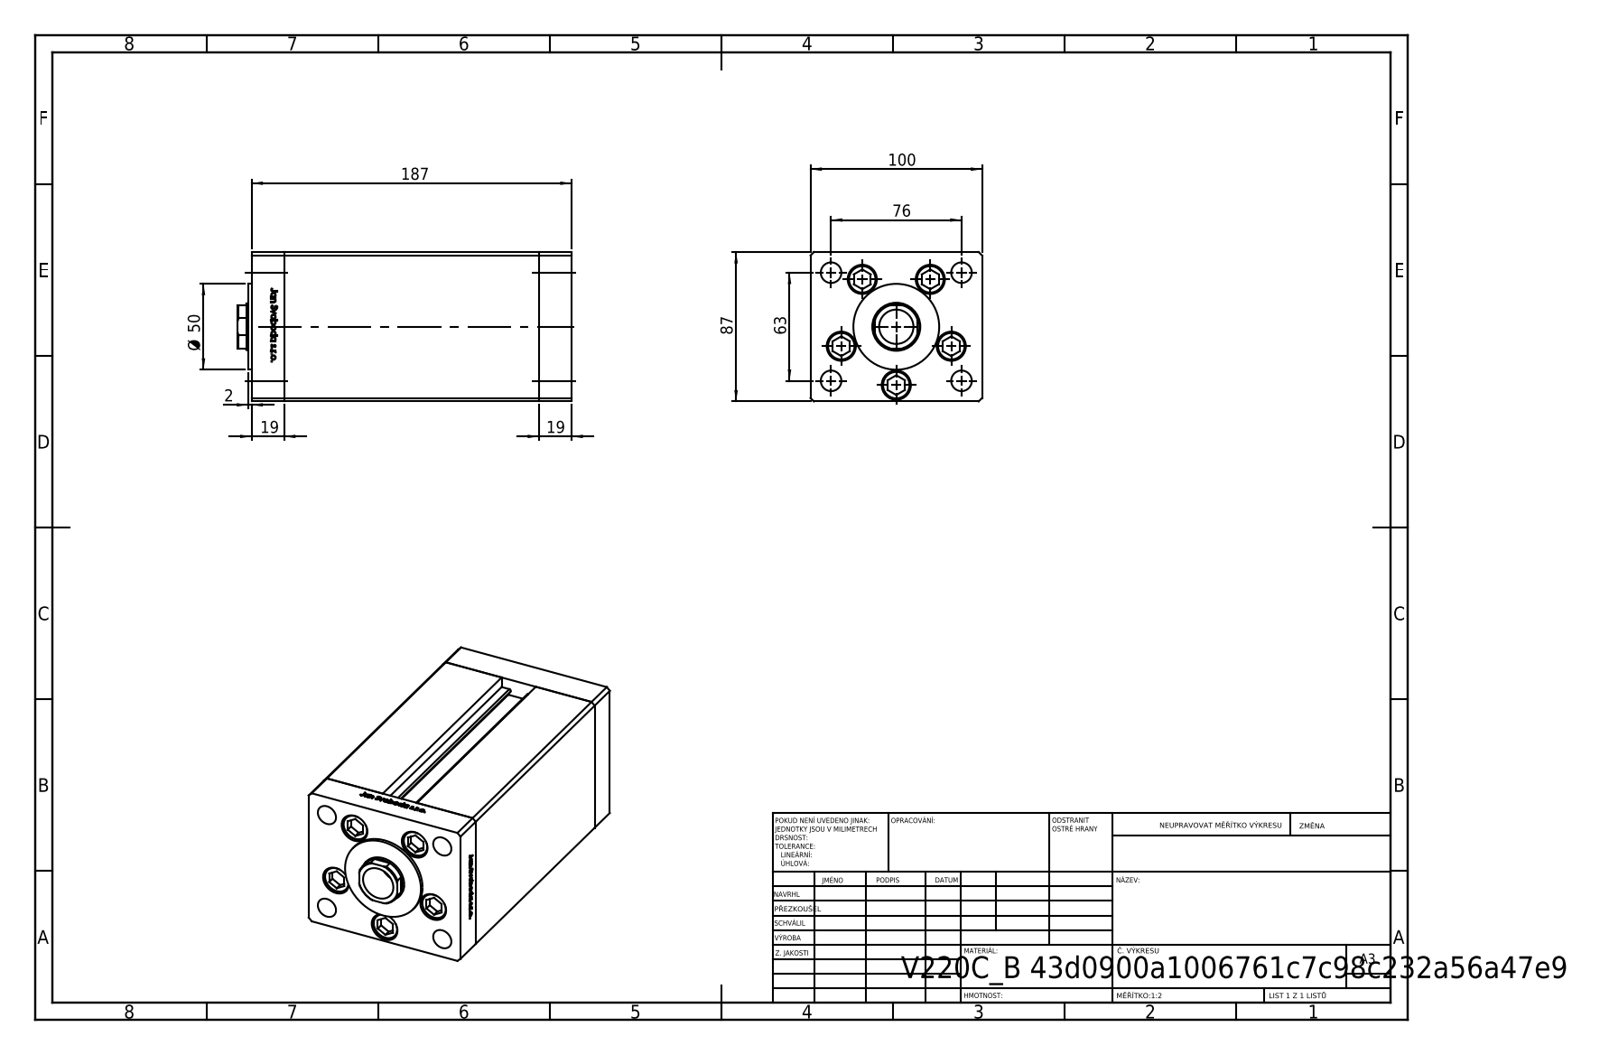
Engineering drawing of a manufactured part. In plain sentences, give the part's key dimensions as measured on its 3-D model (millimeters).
The part is named "ALLEN BOLT; V220C_B_VC; V220C BACK_B; V220C_B MIDDLE (+1 more)". Its 3-D file was written by "SolidWorks 2019 (CONFIG_CONTROL_DESIGN)". It is 14 solids with 1175 faces: 460 planar, 143 cylindrical and 572 other. Overall it measures 194.5 by 100 by 87 millimeters. Its volume is 1 432 000 cubic millimeters and its surface area 200 999 square millimeters. Round holes: 7 of diameter 13.5, 5 of diameter 17, 4 of diameter 12, 2 of diameter 2, 2 of diameter 13.16, 1 of diameter 20, 1 of diameter 28. Round bosses or shafts: 5 of diameter 8, 2 of diameter 17, 1 of diameter 50. Partial cylindrical surfaces (rounded edges, fillets, slot ends): 2 of radius 0.93, 1 of radius 13.5. The main face-to-face distances are 100, 87, 148.5, 19, 167.5, 186.5, 9, 10, 177.5, 158.5. The hole center spacings are 34, 18.59, 39.64, 49.36, 57.95, 21.03, 38.08, 39.27.
